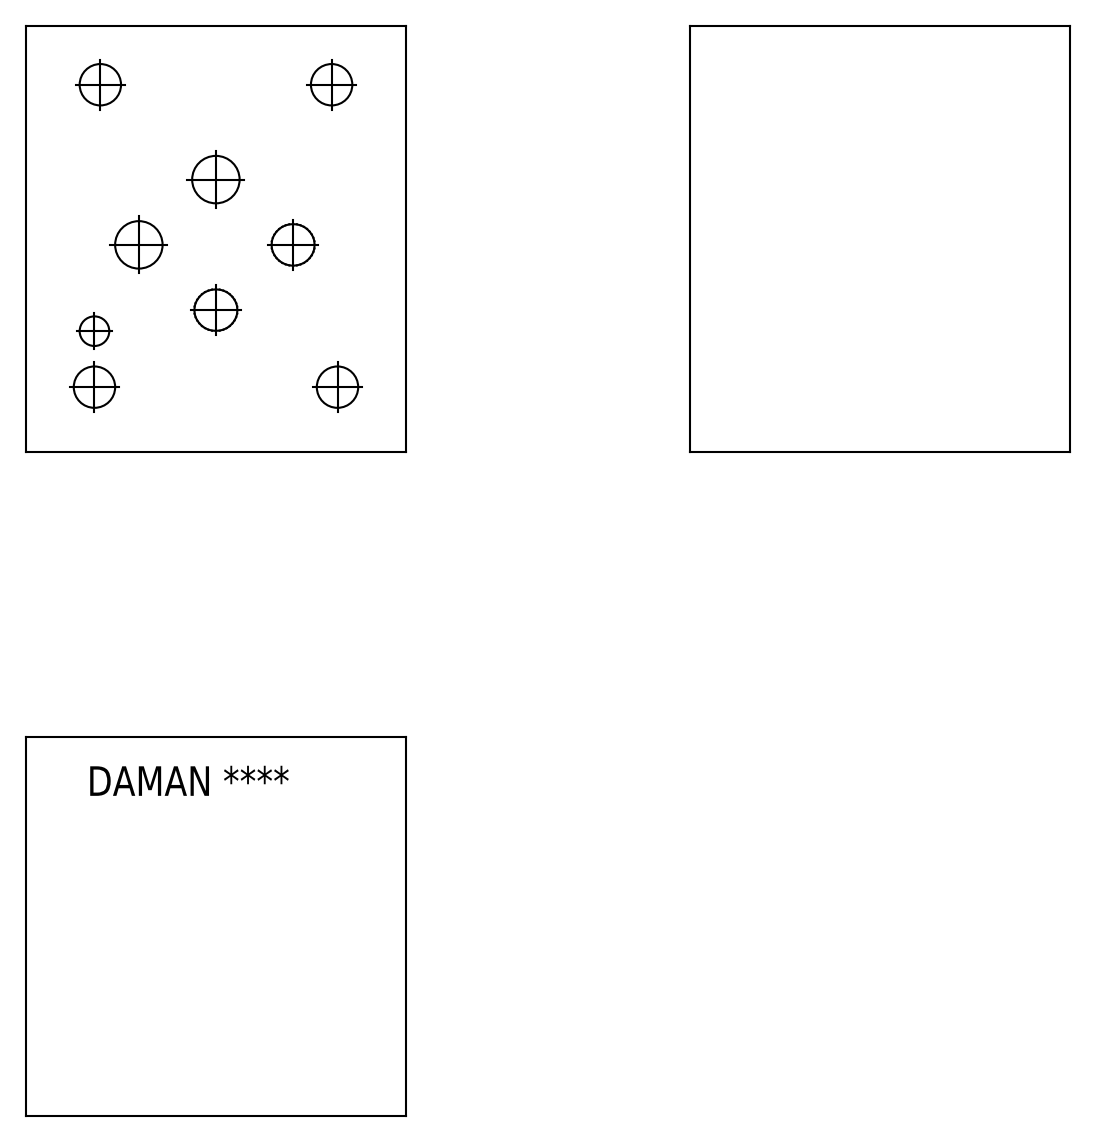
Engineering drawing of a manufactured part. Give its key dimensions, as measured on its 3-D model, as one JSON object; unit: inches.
{"part_name": "Part_AD03D03VABA.B00462R3_3D", "step_written_by": "Autodesk Inventor 2019 (AUTOMOTIVE_DESIGN)", "units": "inches", "bodies": {"solids": 1, "faces": 389, "planar": 249, "cylindrical": 22, "other": 118}, "overall_size": [2.25, 2, 2], "volume_in3": 8.906, "surface_area_in2": 27.66, "round_holes": [[0.219, 8], [0.25, 4], [0.5, 4], [0.125, 1], [0.156, 1]], "face_to_face_distances": [2, 2.25, 0.04, 1.96, 0.039, 2.21, 0.098, 0.13, 0.216, 0.245], "hole_center_spacings": [0.532, 0.65, 0.813, 1.142, 0.533, 0.533, 0.785, 1.321]}
